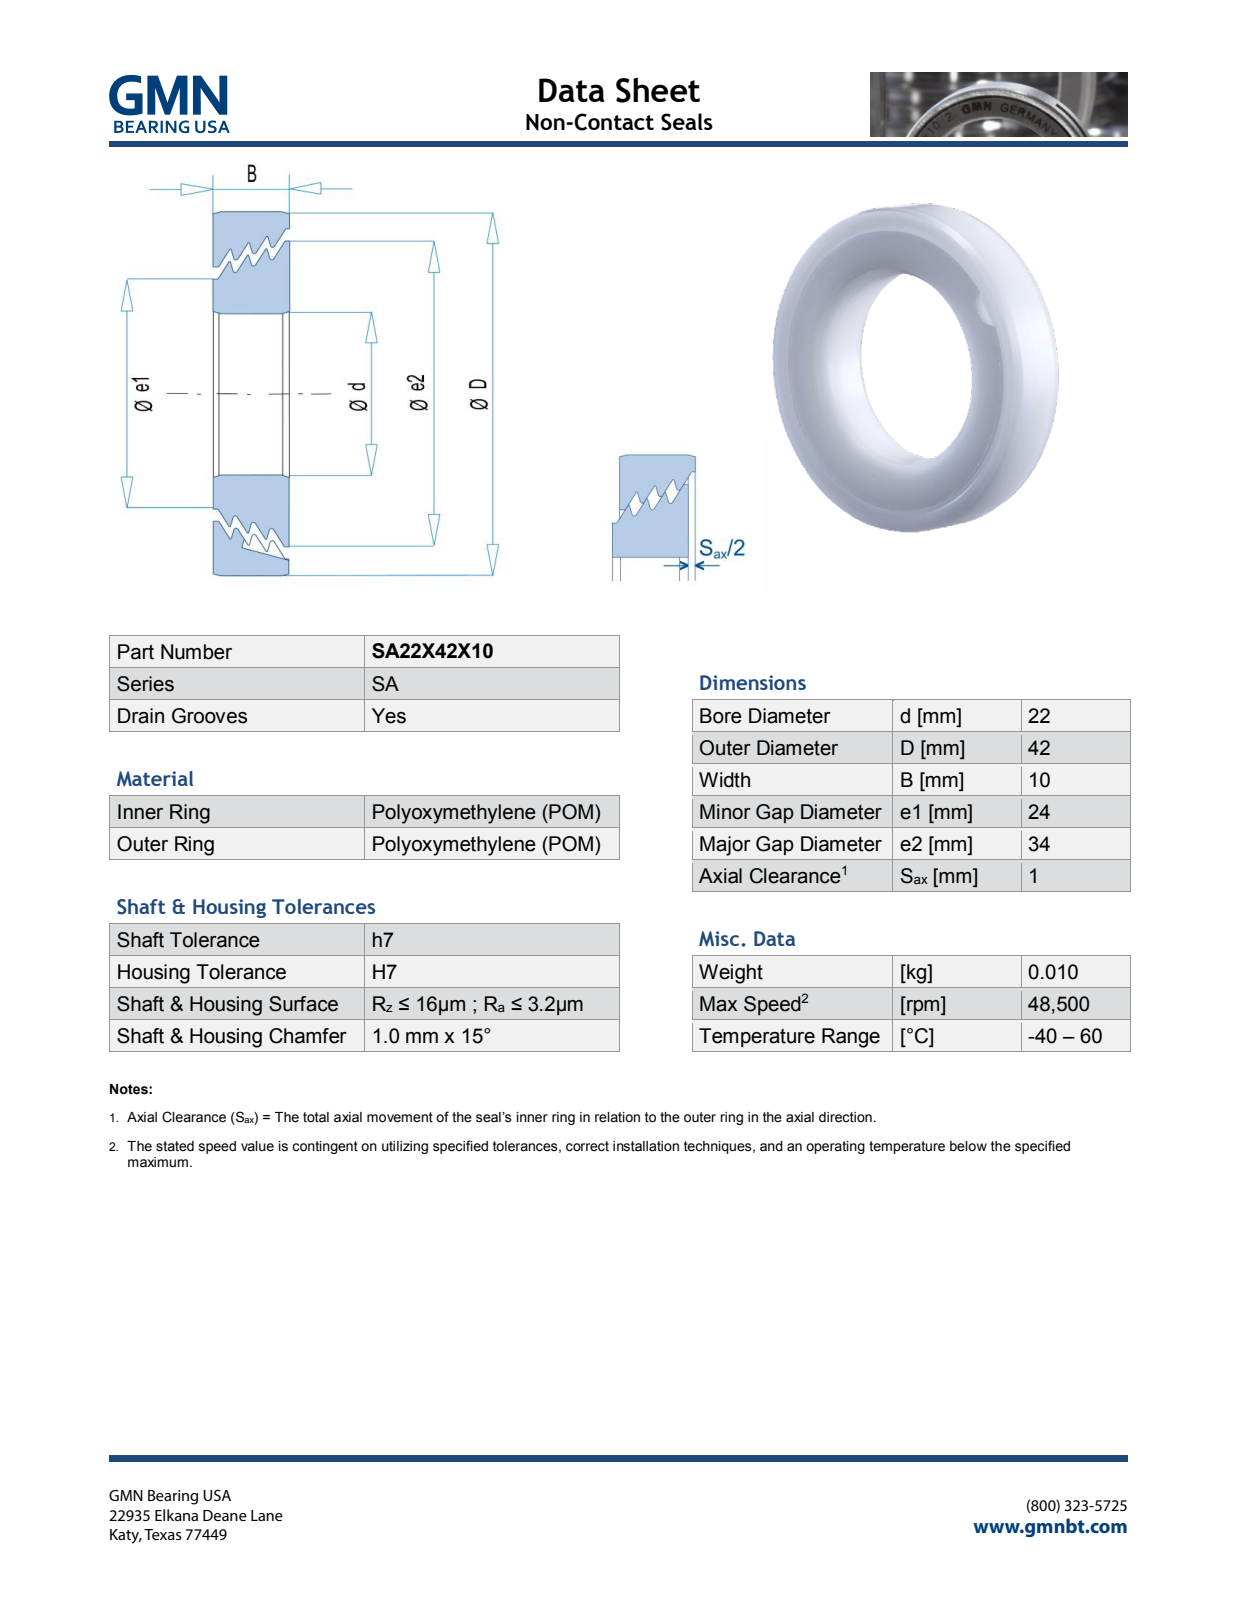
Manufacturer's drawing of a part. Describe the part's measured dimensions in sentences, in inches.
The part is named "SA22X42X10_PRT". Its 3-D file was written by "PRO/ENGINEER BY PARAMETRIC TECHNOLOGY CORPORATION, 2013150 (AUTOMOTIVE_DESIGN)". It is 2 solids with 607 faces: 530 planar, 15 cylindrical and 62 other. Overall it measures 1.654 by 1.654 by 0.396 inches. Its volume is 0.561 cubic inches and its surface area 11.79 square inches. Round holes: 1 of diameter 0.866, 1 of diameter 1.009, 1 of diameter 1.403. Round bosses or shafts: 1 of diameter 1.654, 1 of diameter 1.339, 1 of diameter 0.945. Partial cylindrical surfaces (rounded edges, fillets, slot ends): 1 of radius 0.236. The main face-to-face distances are 0.394, 0.396, 0.06, 0.053, 0.045, 0.043, 0.045, 0.026, 0.061, 0.035.
